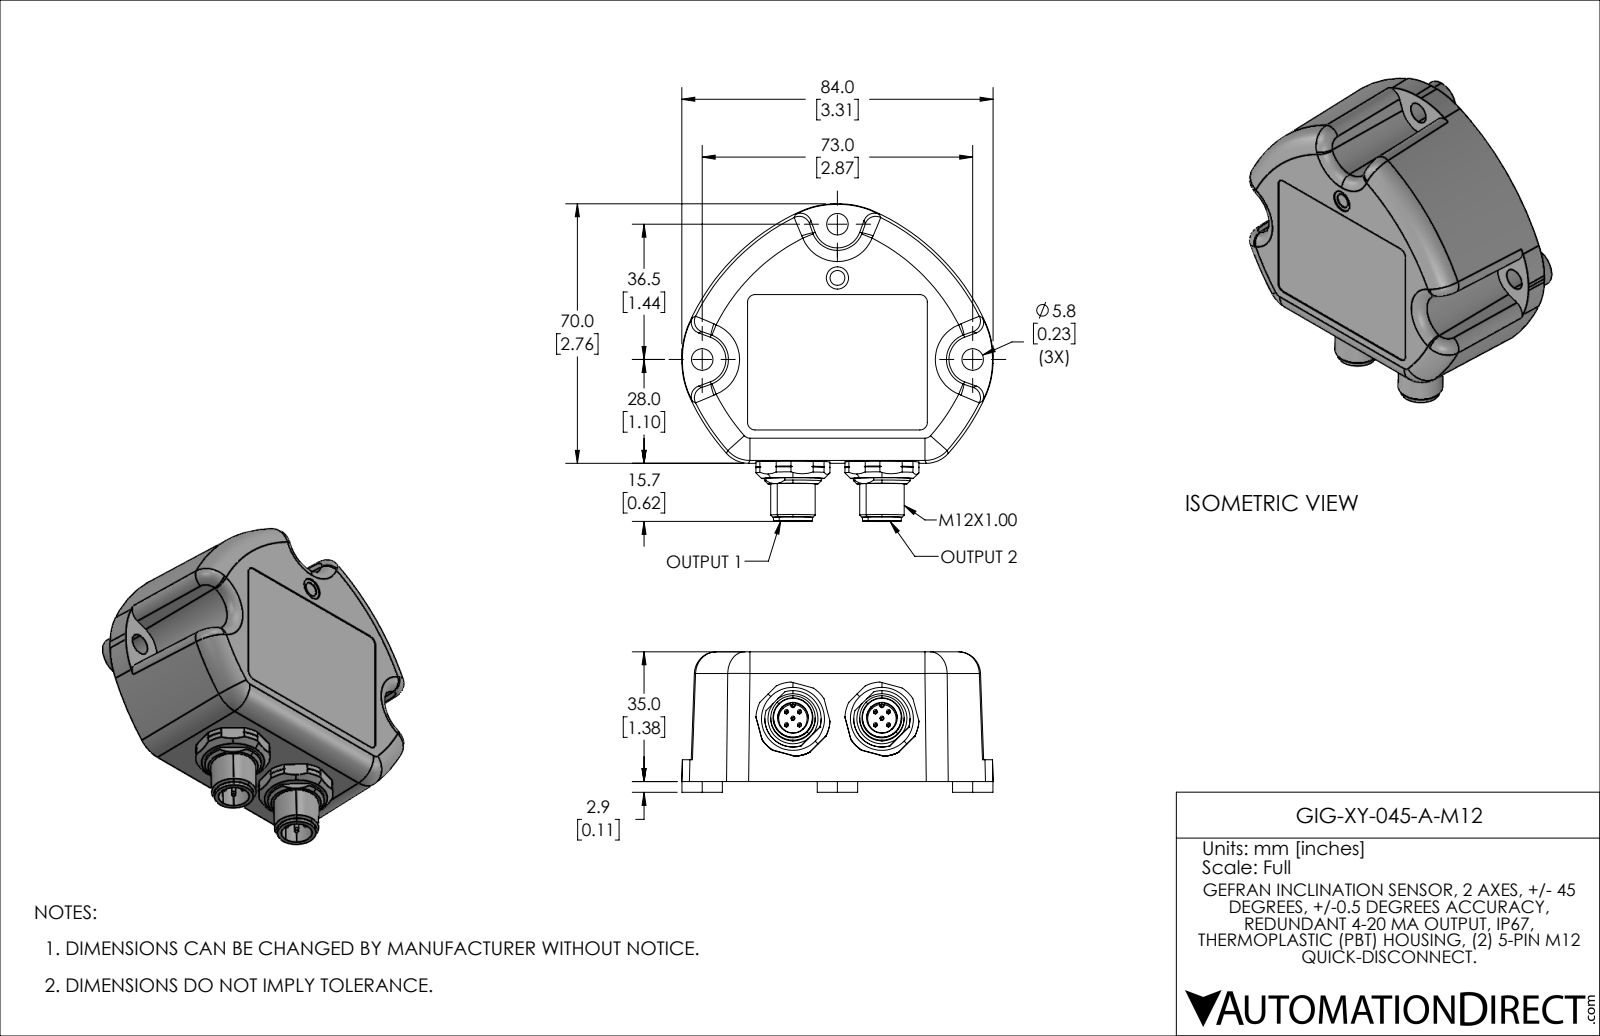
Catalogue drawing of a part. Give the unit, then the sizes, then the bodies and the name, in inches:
Units: inches
Overall size (bounding box): 3.374 × 3.307 × 1.492
Round holes (diameter × count): ⌀0.228 ×3, ⌀0.327 ×2, ⌀0.157 ×1, ⌀0.236 ×1
Round bosses / shafts (diameter × count): ⌀0.039 ×10, ⌀0.429 ×3, ⌀0.472 ×2, ⌀0.413 ×2
Partial cylindrical surfaces — rounded edges, fillets, slot ends (radius × count): R0.02 ×4, R0.079 ×4, R0.299 ×3, R0.024 ×2, R0.273 ×2, R0.394 ×2, R0.236 ×1, R0.301 ×1
Main face-to-face distances: 1.37, 1.378, 0.232, 1.138, 1.146, 0.114, 0.346, 1.484, 1.492, 0.668
Hole centre spacings: 1.678, 2.032, 0.571, 0.945, 2.874
Volume: 9.029 in³ · Surface area: 32.38 in²
Bodies: 1 solid, 365 faces (87 planar, 123 cylindrical, 155 other)
Part name (STEP PRODUCT): GIG-XY-045-A-M12
STEP written by: SolidWorks 2021 (AUTOMOTIVE_DESIGN)
